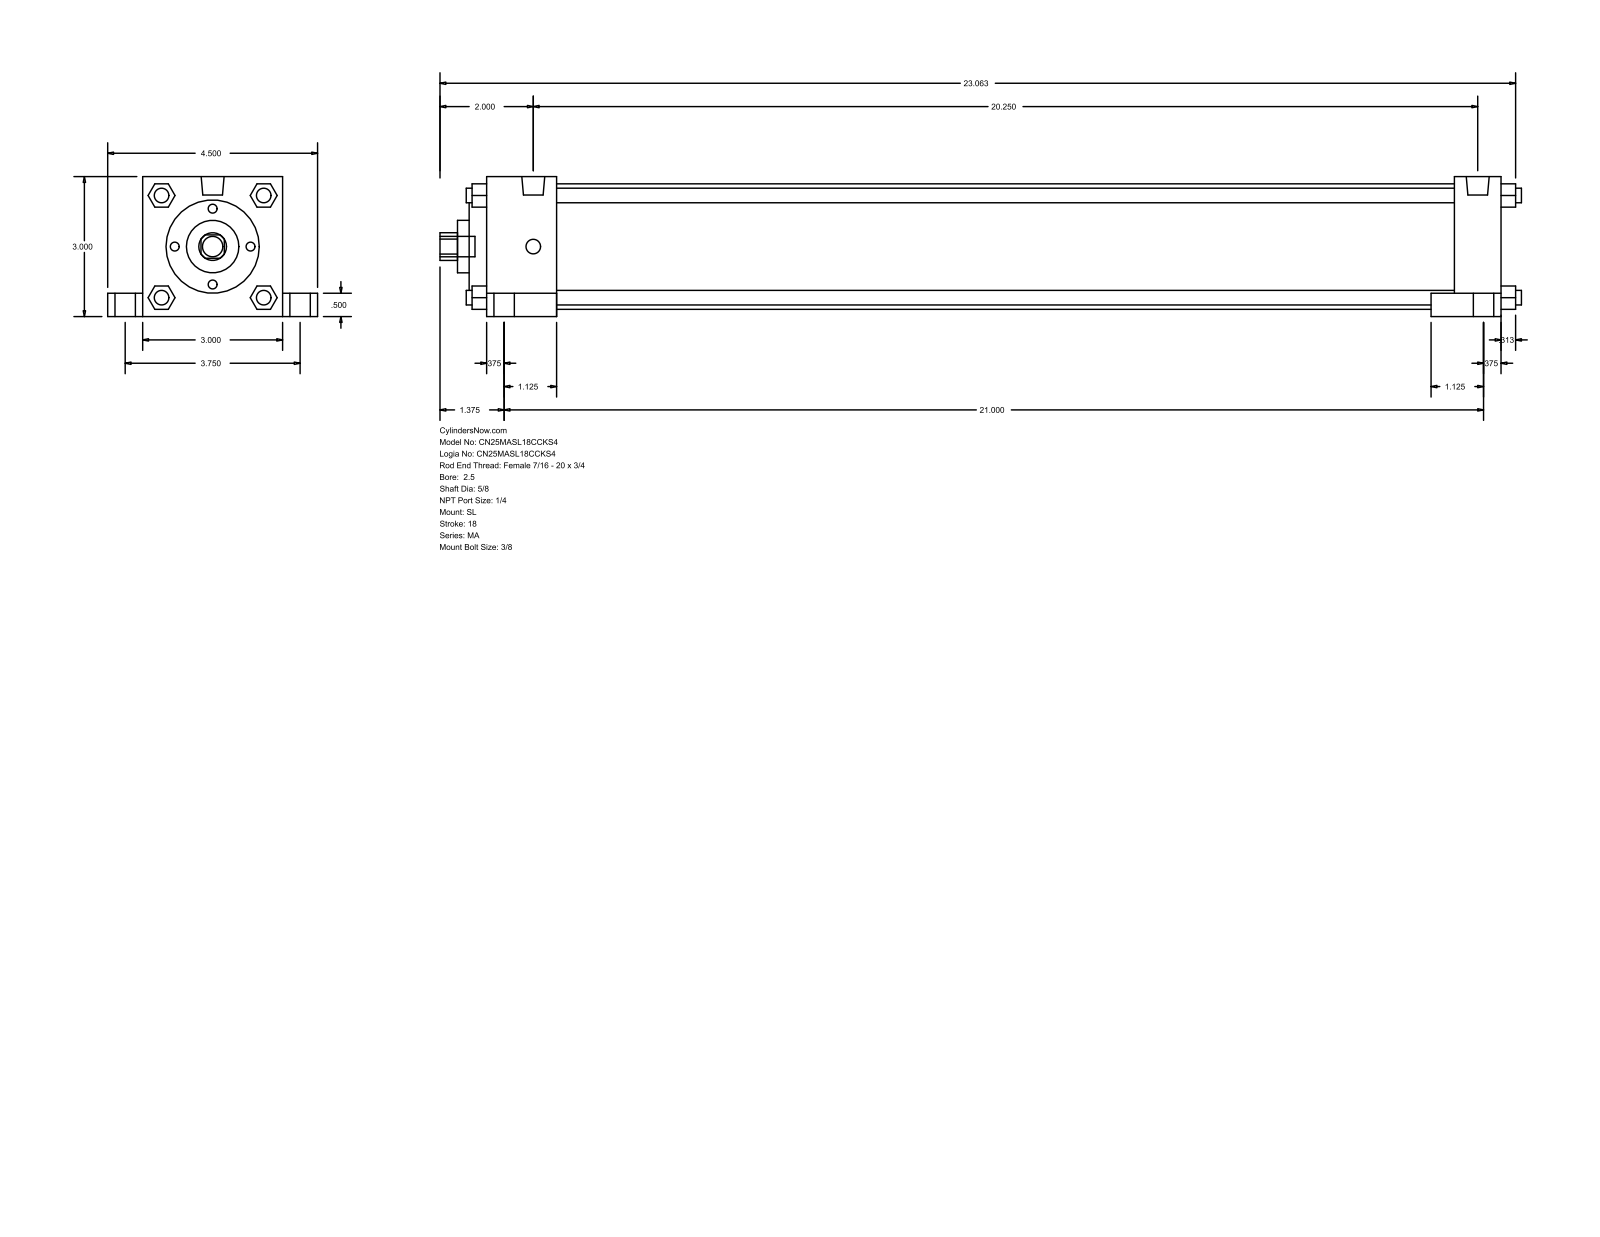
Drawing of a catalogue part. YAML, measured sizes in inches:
part_name: "MA_SL__0250_0.625"
step_written_by: "GSSL Pune (CONFIG_CONTROL_DESIGN)"
units: inches
bodies: {solids: 0, faces: 150, planar: 113, cylindrical: 37, other: 0}
overall_size: [23.187, 4.5, 3]
round_holes:
  - {diameter: 0.625, count: 1}
  - {diameter: 1.125, count: 1}
  - {diameter: 2, count: 1}
  - {diameter: 2.69, count: 1}
round_bosses_or_shafts:
  - {diameter: 0.313, count: 8}
  - {diameter: 0.437, count: 5}
  - {diameter: 0.687, count: 4}
  - {diameter: 0.492, count: 2}
partial_cylinders:
  - {radius: 0.297, count: 1}
face_to_face_distances: [3, 21.75, 0.5, 19.25, 1, 1.5, 20.25, 20.75, 0.75, 2.5]
